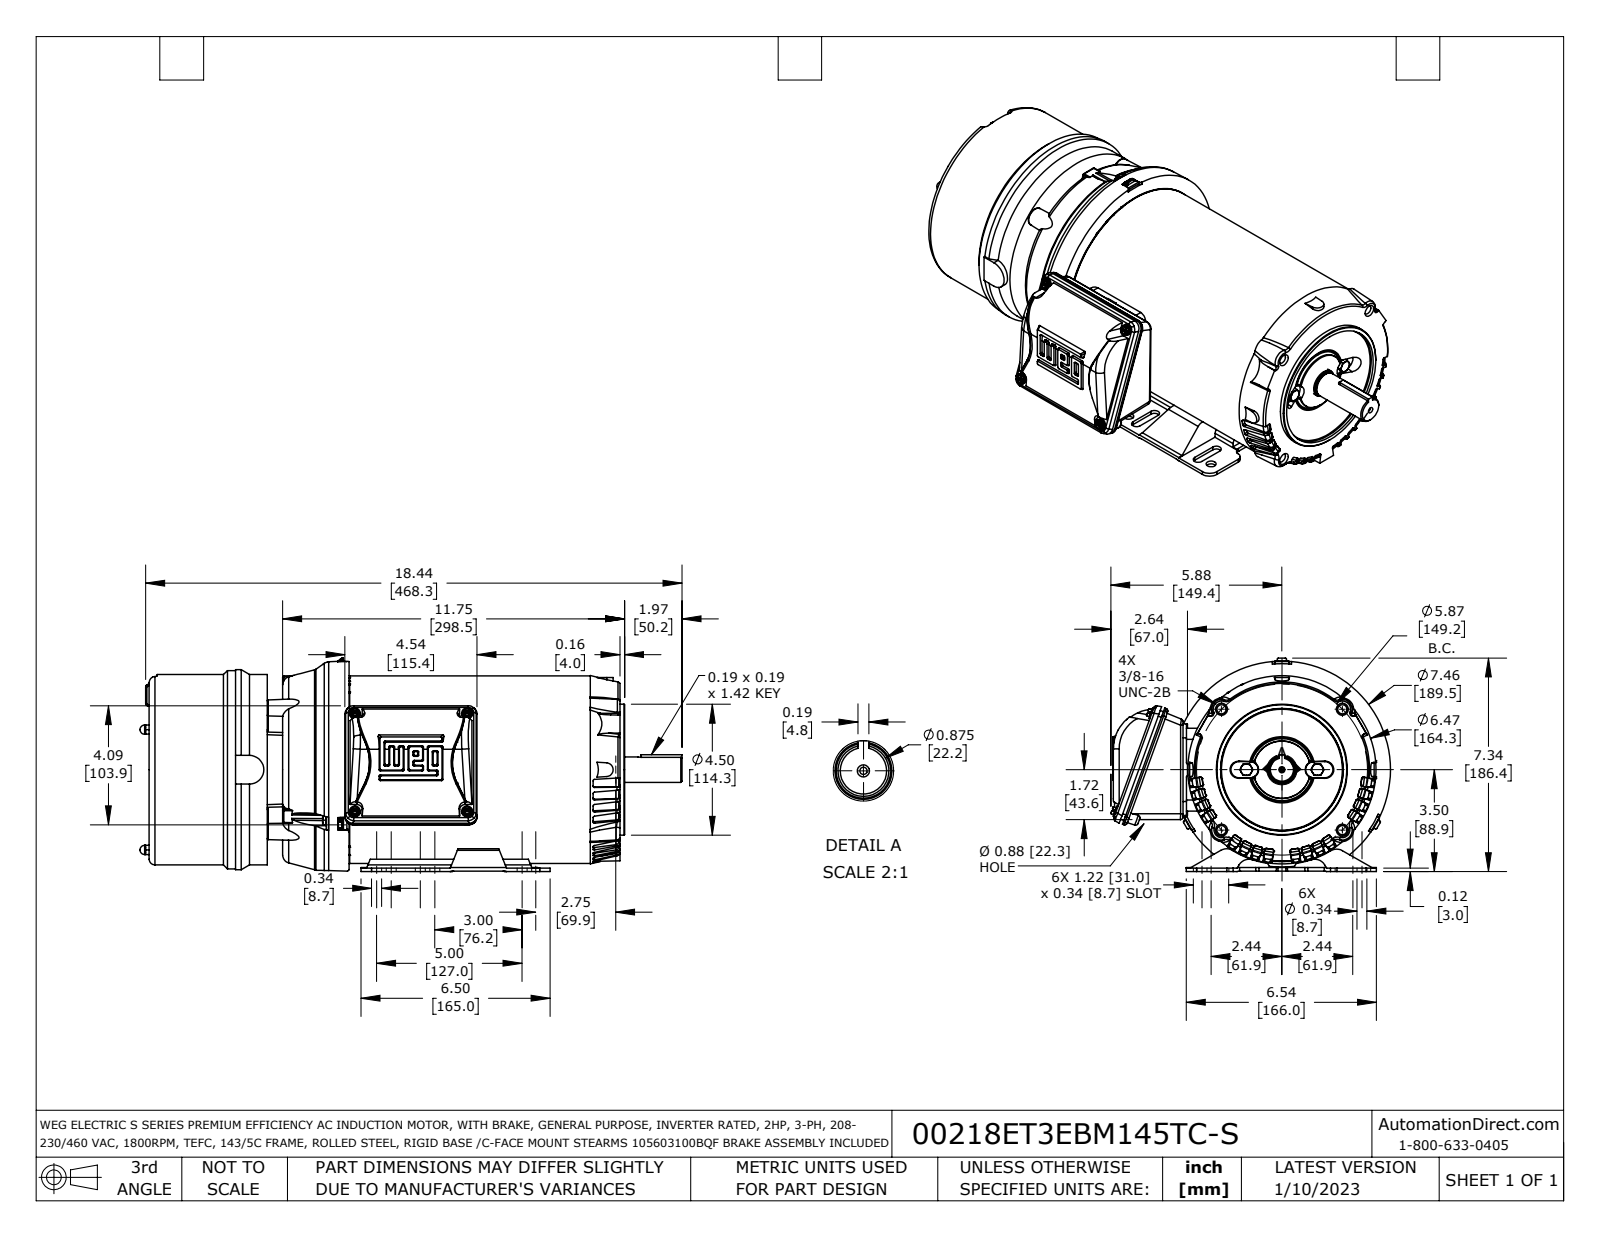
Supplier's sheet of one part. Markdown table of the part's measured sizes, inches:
| quantity | value |
| --- | --- |
| part name | 143-5C_3PH_TEFC_BM_188779 new 09-26-22 broken base surfs w 1PHNB coord fxt |
| STEP written by | SolidWorks 2021 (AUTOMOTIVE_DESIGN) |
| units | inches |
| bodies | 16 solids, 1591 faces (610 planar, 427 cylindrical, 554 other) |
| overall size | 18.632 × 9.612 × 7.338 |
| volume | 570.5 in³ |
| surface area | 875.2 in² |
| round holes (diameter × count) | 0.343 × 6, 0.313 × 4, 0.124 × 1 |
| round bosses / shafts (diameter × count) | 0.374 × 4, 0.315 × 3, 0.256 × 3, 0.35 × 2, 6.87 × 1, 6.811 × 1, 6.54 × 1, 6.457 × 1 |
| partial cylindrical surfaces (radius × count) | 0.039 × 51, 0.047 × 40, 0.051 × 32, 0.02 × 16, 0.079 × 14, 0.087 × 12, 0.171 × 12, 0.197 × 9 |
| main face-to-face distances | 8.268, 11.102, 2.835, 4.059, 6.894, 15.161, 4.591, 0.531, 2.303, 10.571 |
| hole center spacings | 2.937, 4.154, 5.5, 1, 4, 5, 5.59, 5.874 |
